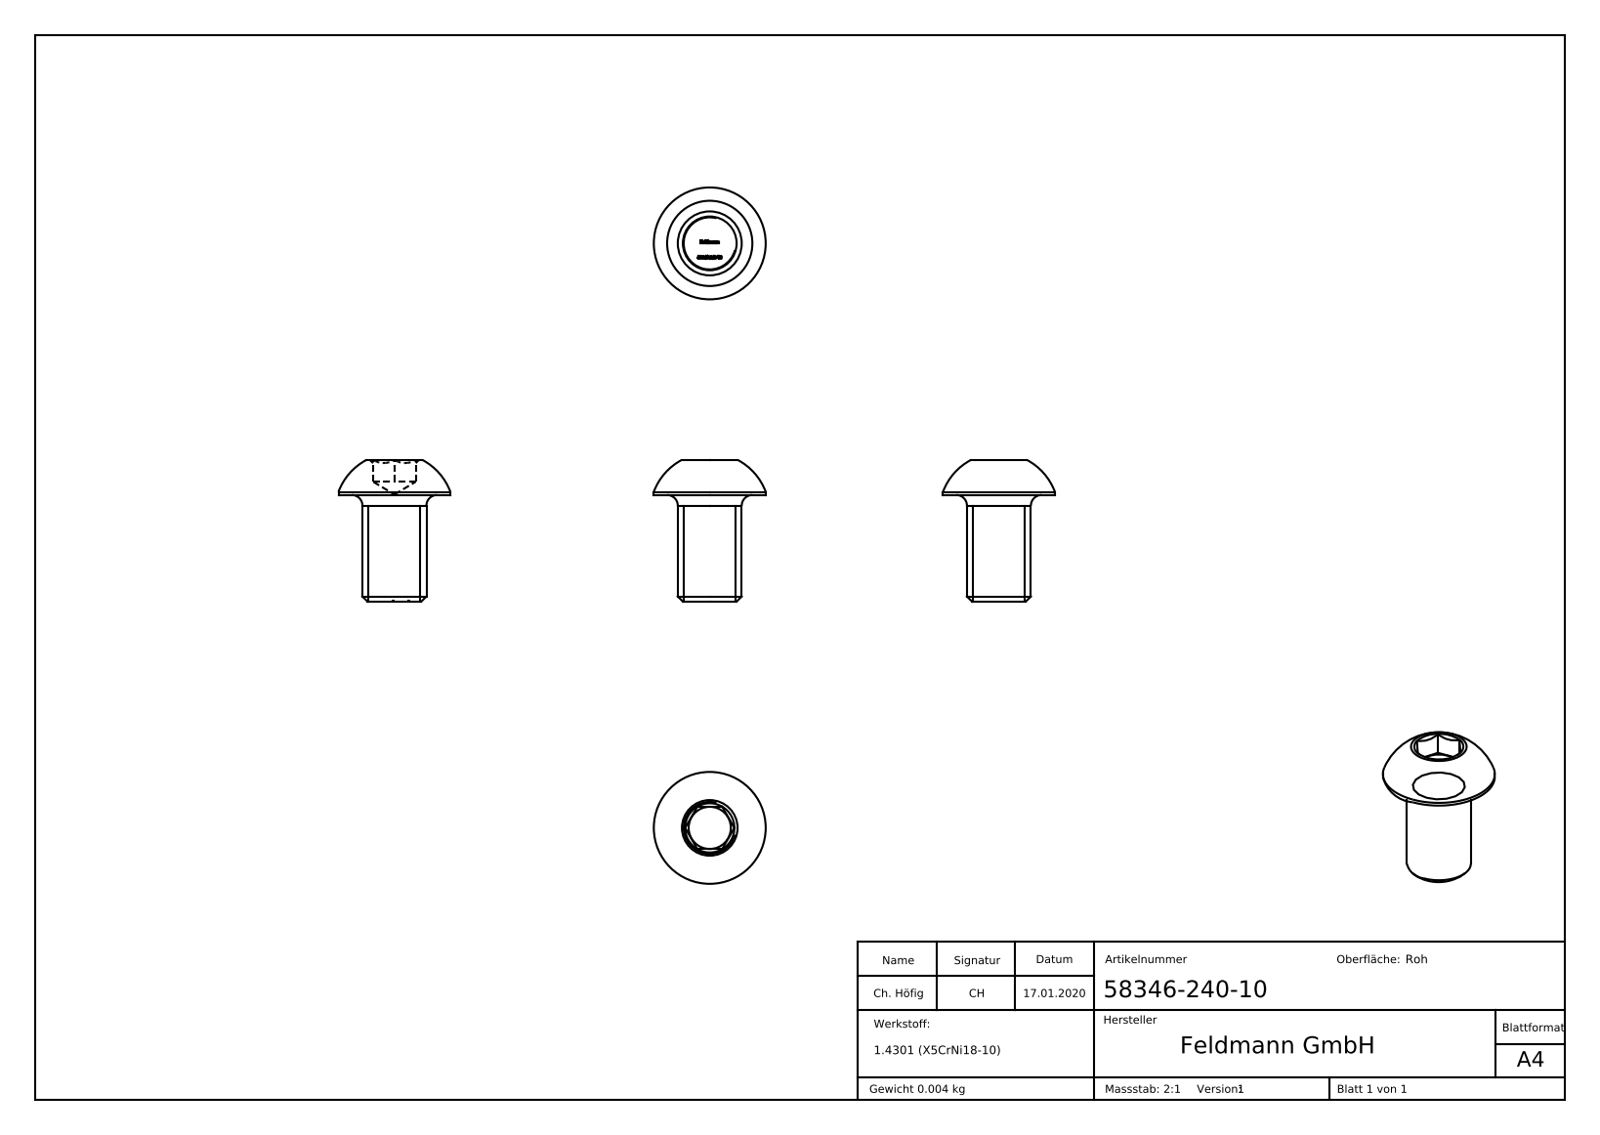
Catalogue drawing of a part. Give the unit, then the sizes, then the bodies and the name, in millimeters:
Units: millimetres
Overall size (bounding box): 18 × 10.5 × 10.5
Round bosses / shafts (diameter × count): ⌀10.5 ×1, ⌀6 ×1
Main face-to-face distances: 10, 4, 3.3, 13.3, 1.24, 2.06, 11.24, 13.2, 11.14, 9.9
Volume: 453 mm³ · Surface area: 430 mm²
Bodies: 1 solid, 284 faces (152 planar, 2 cylindrical, 130 other)
Part name (STEP PRODUCT): 58346-240-10
STEP written by: SolidWorks 2015 (CONFIG_CONTROL_DESIGN)
